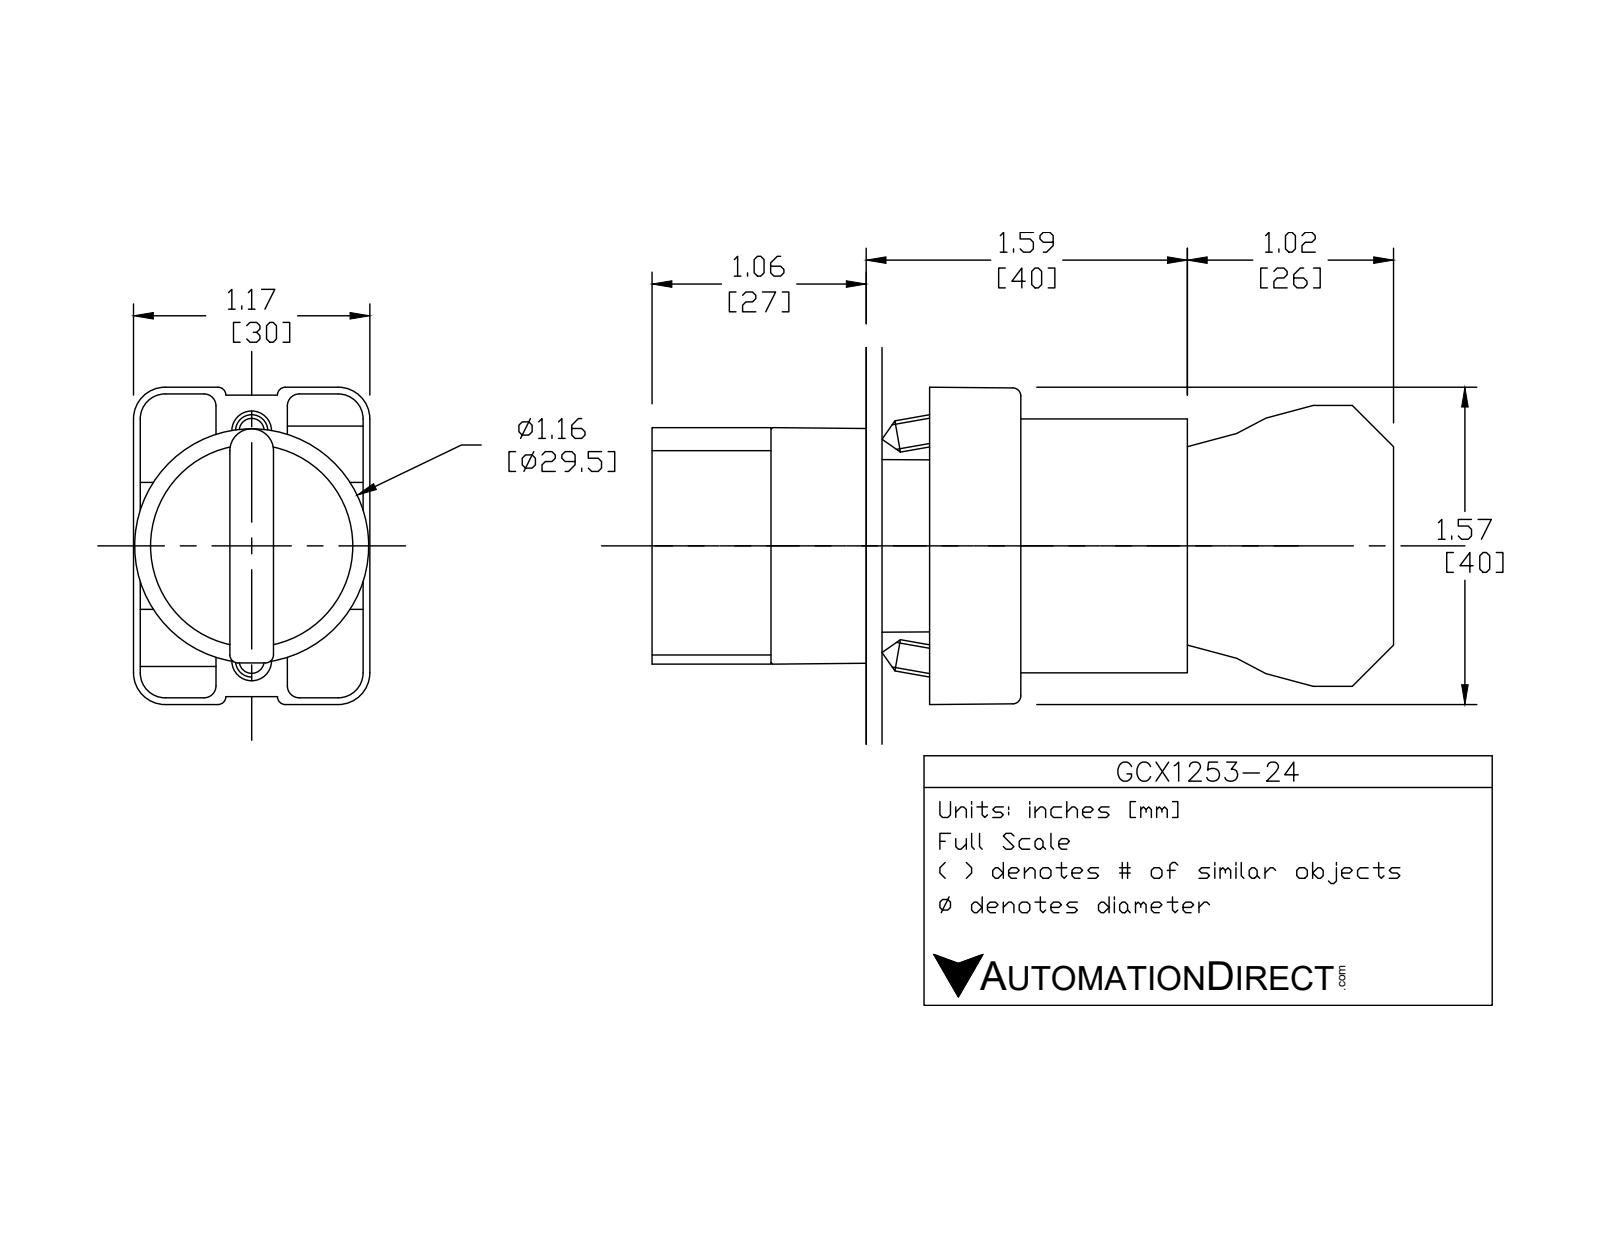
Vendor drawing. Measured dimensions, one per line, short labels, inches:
name: GCX1253-24; GCX1253 OPERATOR; ecx1029; ECX1050 (+1 more)
written by: SolidWorks 2016 (AUTOMOTIVE_DESIGN)
unit: in
bodies: 8 solids, 445 faces (263 planar, 151 cylindrical, 31 other)
size: 3.653 × 1.581 × 1.177
volume: 2.799 in³; area: 39 in²
holes: 2× ⌀0.079, 2× ⌀0.124, 2× ⌀0.13, 1× ⌀0.087, 1× ⌀0.197, 1× ⌀0.469, 1× ⌀0.878, 1× ⌀0.888, 1× ⌀1.024
bosses: 4× ⌀0.157, 1× ⌀1.175, 1× ⌀1.004, 1× ⌀0.945, 1× ⌀0.856, 1× ⌀0.78, 1× ⌀0.504
rounds: 24× R0.059, 12× R0.041, 12× R0.124, 12× R0.157, 9× R0.039, 2× R0.128, 1× R0.02, 1× R0.063
face distances: 0.827, 2.02, 1.193, 0.579, 1.244, 1.171, 0.472, 0.469, 0.031, 0.033
hole spacings: 0.236, 0.544, 0.472, 0.49
